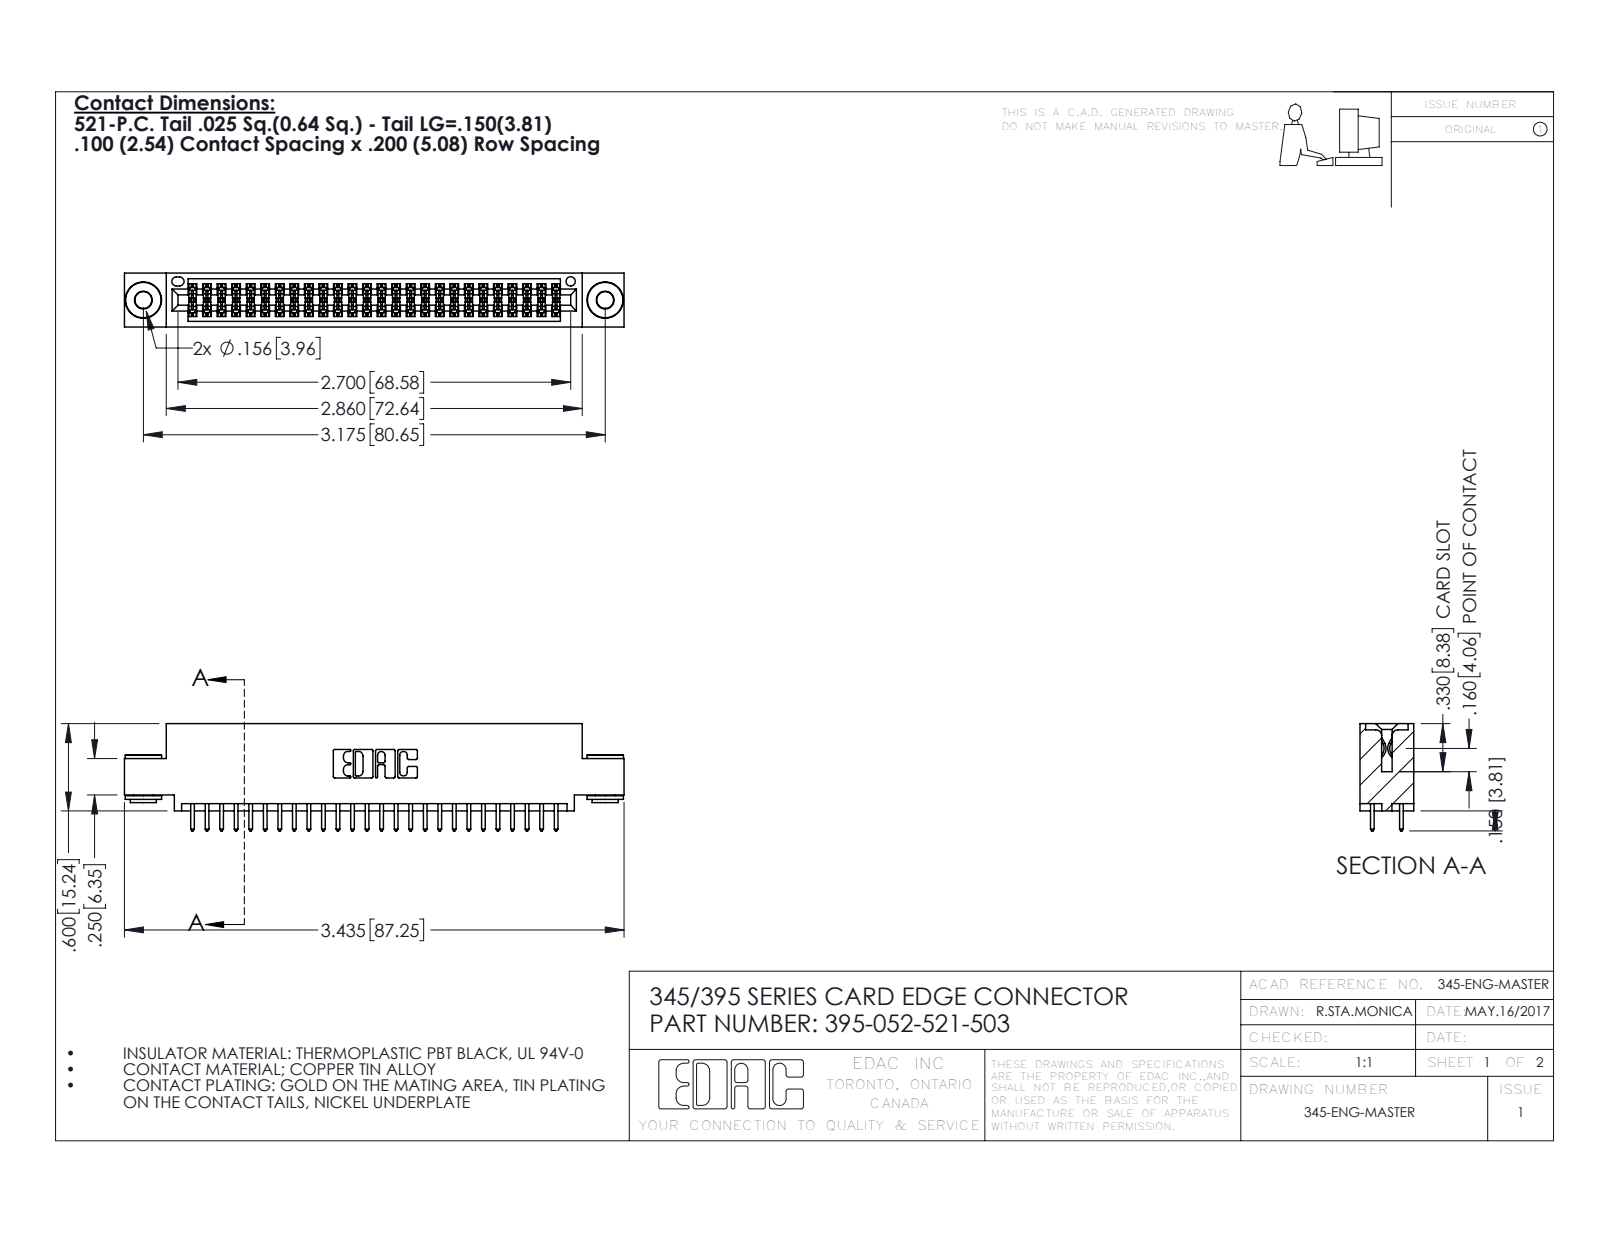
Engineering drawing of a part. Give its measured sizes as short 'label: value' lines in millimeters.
name: 345-250-002_345-250-002-102; 345 Part_0.110 Offset - 0.156 Dia-TH; 395-052-521-503; 345-292-001_345-293-121
written by: SolidWorks 2016 (CONFIG_CONTROL_DESIGN)
unit: mm
bodies: 55 solids, 2768 faces (1810 planar, 950 cylindrical, 8 other)
size: 87.2 × 18.7 × 9.4
volume: 8 260 mm³; area: 12 050 mm²
holes: 2× ⌀2.9, 2× ⌀4, 1× ⌀1.6
bosses: 2× ⌀6.4, 2× ⌀4.6, 2× ⌀3.5
rounds: 78× R0.2, 52× R0.3, 22× R0.3, 6× R0.2, 6× R0.8, 3× R0.7, 2× R0.4, 2× R0.5
face distances: 1.8, 7.6, 5.1, 0.6, 9.4, 2.5, 6.9, 5.7, 4.4, 3.8
hole spacings: 6.9, 74.7, 80.6
